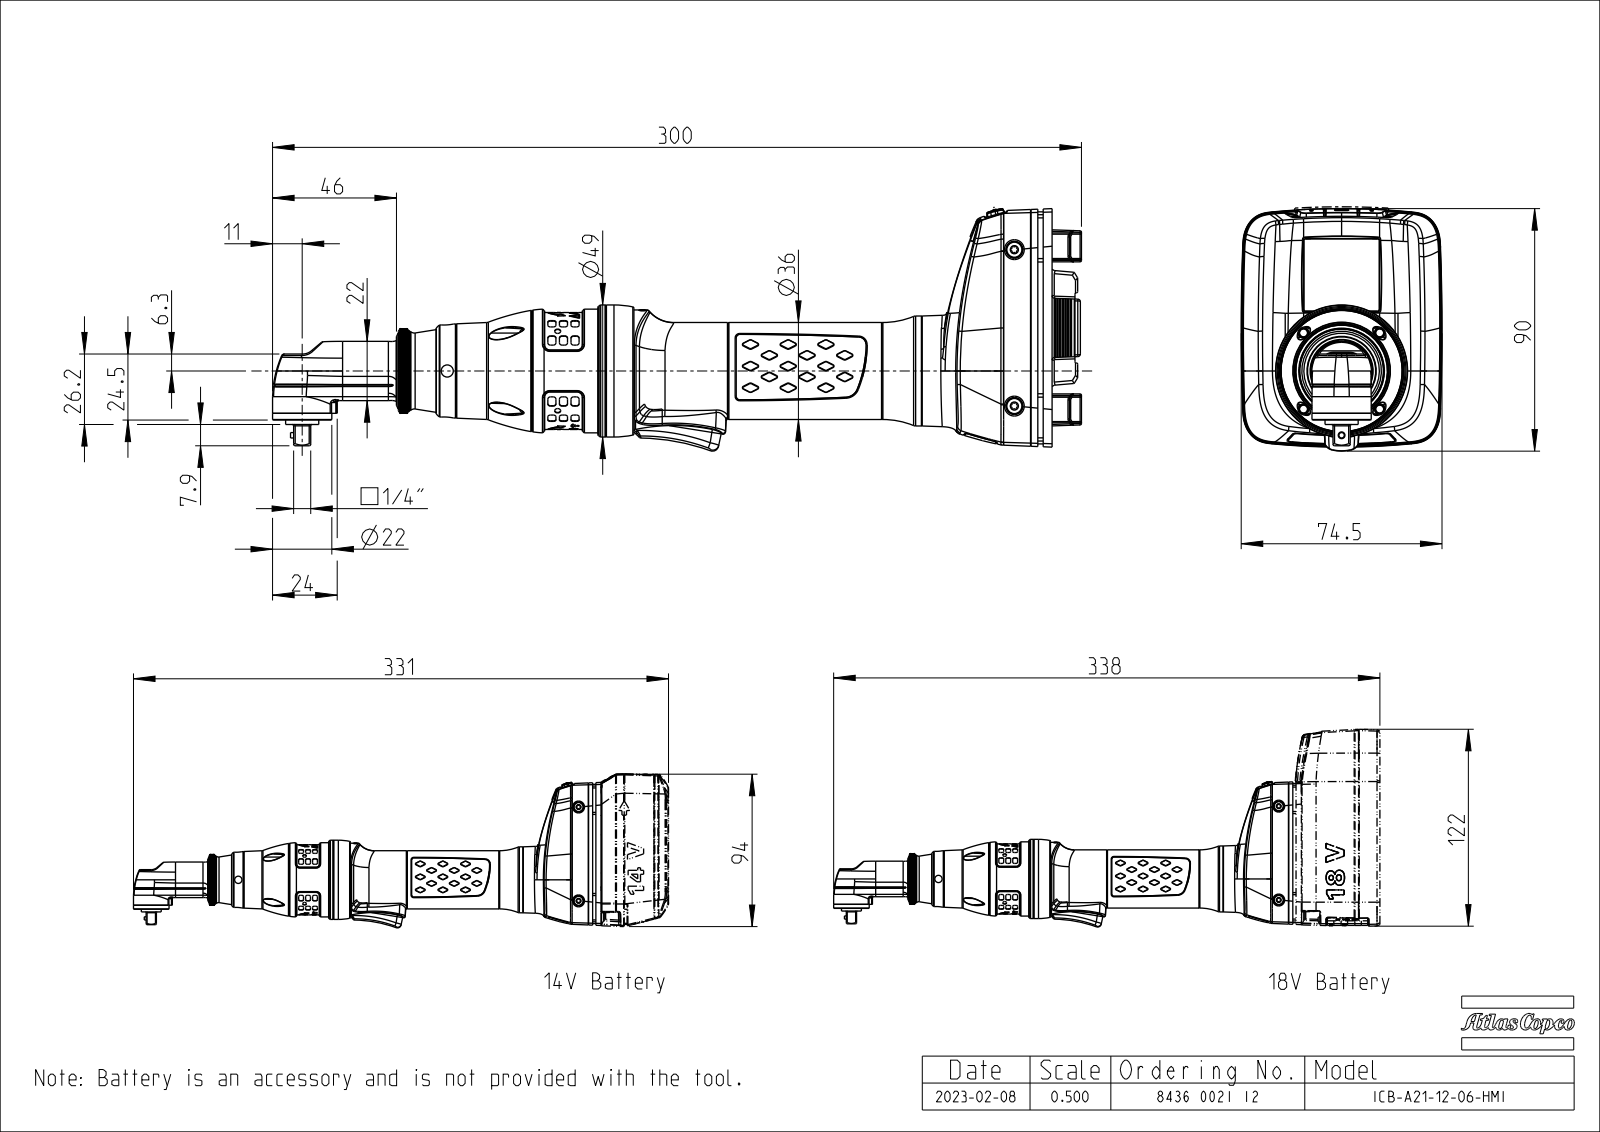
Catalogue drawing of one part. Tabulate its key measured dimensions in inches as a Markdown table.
| quantity | value |
| --- | --- |
| part name | EXT_COMP_SW0014 |
| STEP written by | CREO PARAMETRIC BY PTC INC, 2020281 (CONFIG_CONTROL_DESIGN) |
| units | inches |
| bodies | 7 solids, 17790 faces (8592 planar, 3120 cylindrical, 6078 other) |
| overall size | 11.823 × 3.543 × 2.935 |
| volume | 17.38 in³ |
| surface area | 204.5 in² |
| round holes (diameter × count) | 0.098 × 7, 0.081 × 4, 0.087 × 4, 0.102 × 4, 0.13 × 4, 0.169 × 4, 0.126 × 3, 0.177 × 3, 0.079 × 2, 0.043 × 1, 0.063 × 1, 0.114 × 1 |
| round bosses / shafts (diameter × count) | 0.315 × 4, 0.157 × 4, 0.22 × 3, 0.118 × 3, 0.866 × 2, 1.929 × 1, 1.807 × 1, 1.783 × 1 |
| partial cylindrical surfaces (radius × count) | 0.012 × 423, 0.02 × 262, 0.039 × 98, 0.079 × 72, 0.004 × 41, 0.006 × 36, 0.118 × 31, 0.011 × 30 |
| main face-to-face distances | 0.441, 0.797, 0.039, 0.266, 0.795, 0.118, 0.059, 0.098, 0.226, 0.429 |
| hole center spacings | 0.346, 0.49, 0.75, 2.184, 2.294, 3.077, 0.479, 0.693 |
